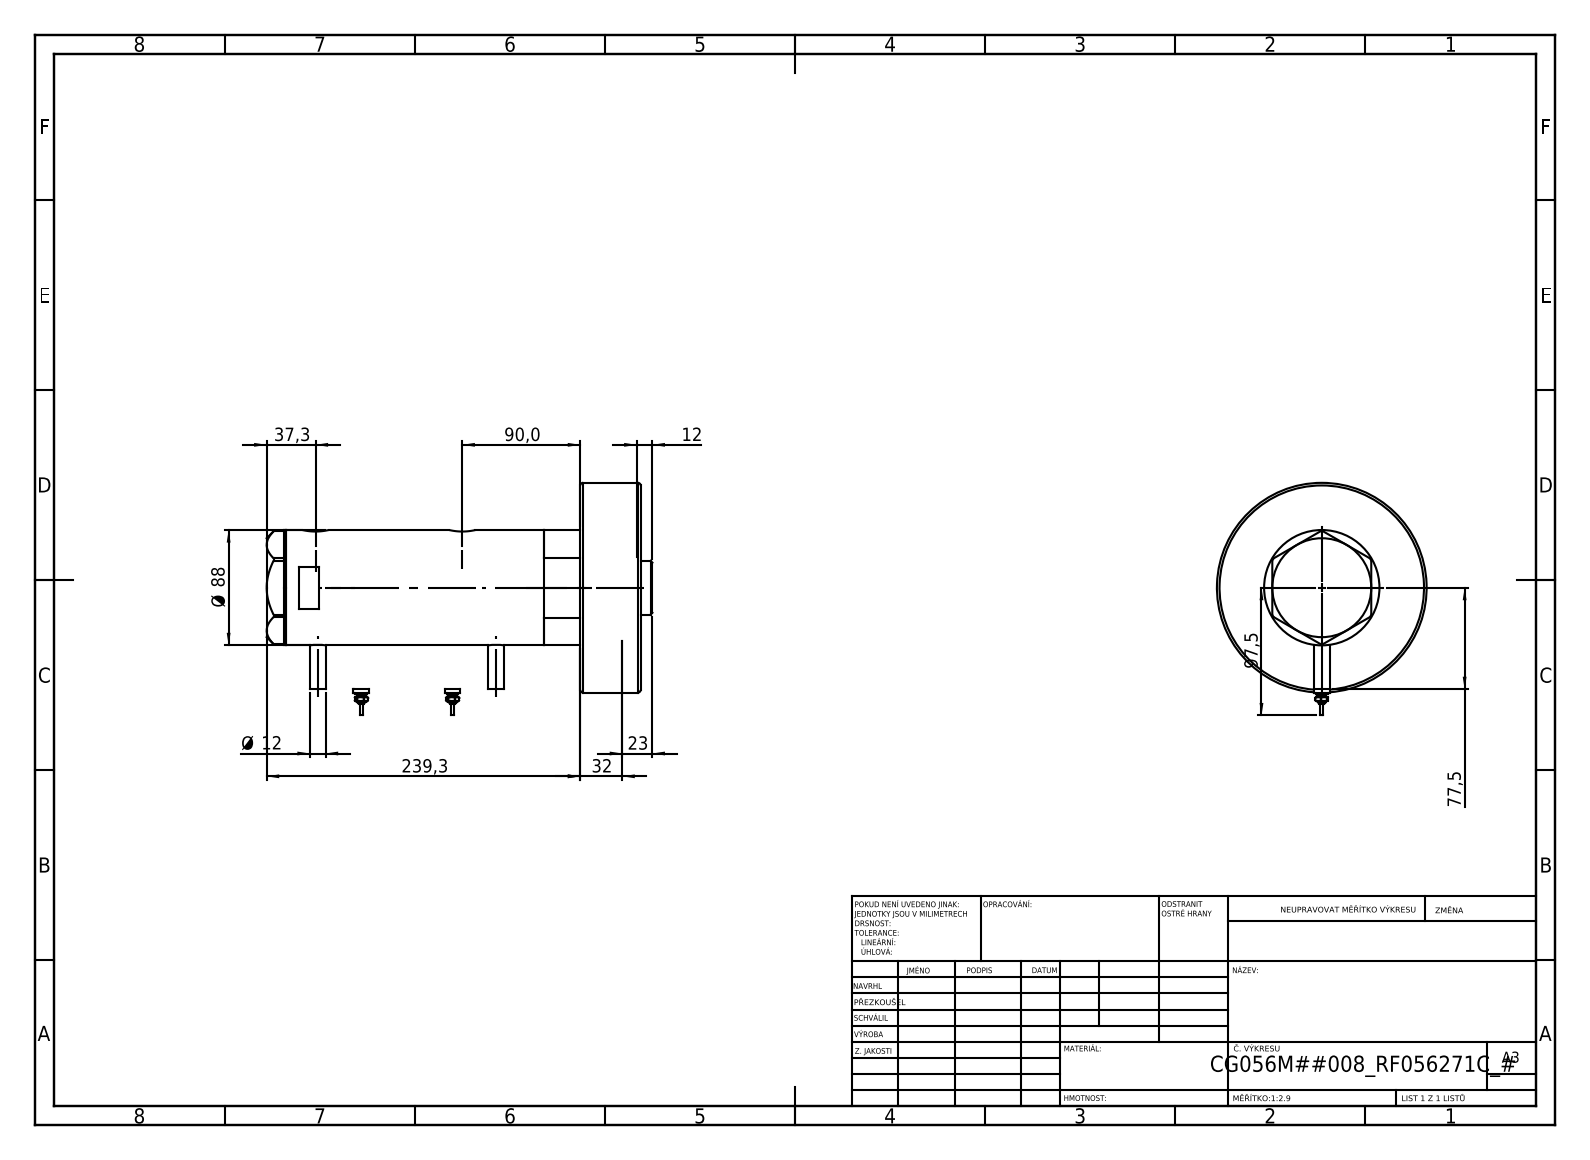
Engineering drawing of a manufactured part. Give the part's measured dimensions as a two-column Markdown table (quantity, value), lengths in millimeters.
| quantity | value |
| --- | --- |
| part name | V270CG_VC; V270CG_FRONT; V270CG_271C; Switch (+2 more) |
| STEP written by | SolidWorks 2019 (CONFIG_CONTROL_DESIGN) |
| units | millimeters |
| bodies | 7 solids, 223 faces (82 planar, 73 cylindrical, 68 other) |
| overall size | 294.3 × 177.5 × 160 |
| volume | 2 307 000 mm³ |
| surface area | 290 907 mm² |
| round holes (diameter × count) | 12.5 × 2, 13.16 × 2, 20 × 2, 14.5 × 1, 42 × 1, 43.5 × 1, 56 × 1, 60 × 1, 75 × 1, 80 × 1 |
| round bosses / shafts (diameter × count) | 12 × 4, 9 × 2, 7 × 2, 4.5 × 2, 2.5 × 2, 160 × 1, 88 × 1, 73 × 1 |
| main face-to-face distances | 46, 224.3, 270.3, 134.4, 89.9, 135.9, 244.3, 26, 108.4, 198.3 |
| hole center spacings | 1.7, 25.8, 110.3, 112, 136.1, 137.8 |
